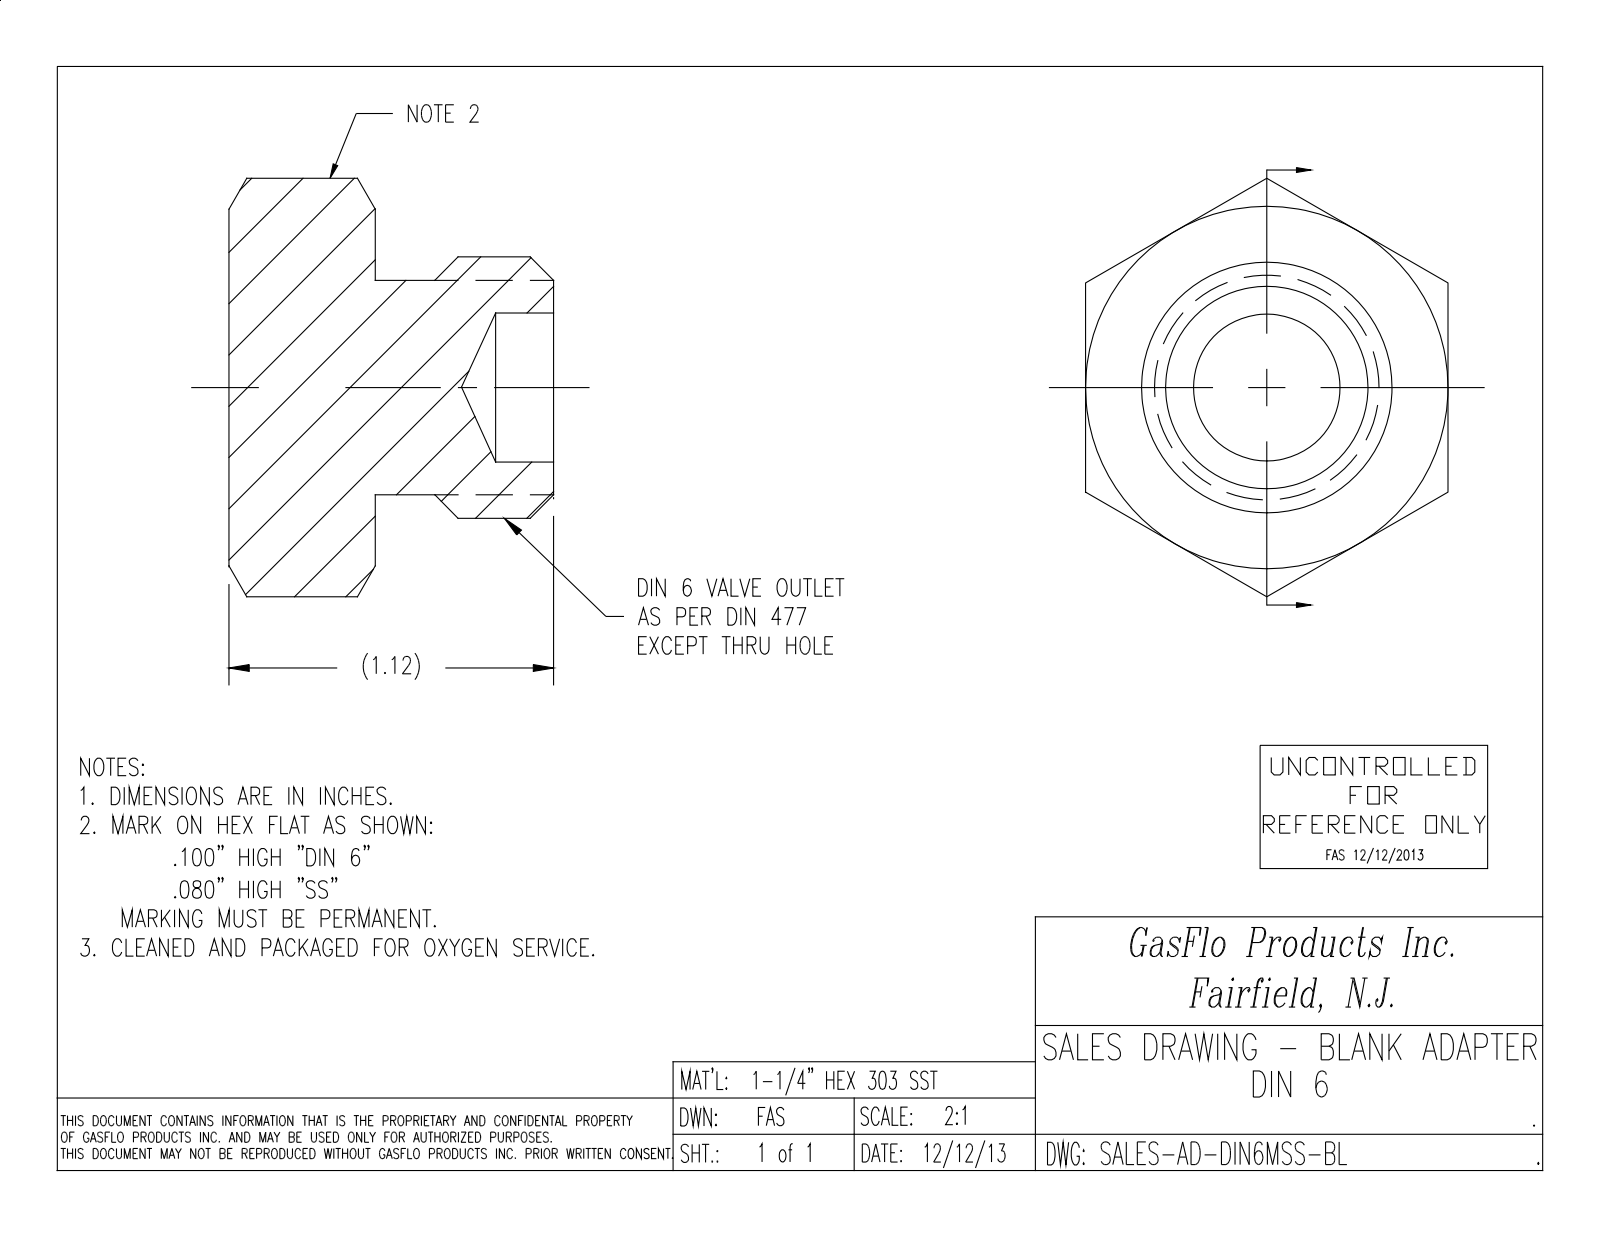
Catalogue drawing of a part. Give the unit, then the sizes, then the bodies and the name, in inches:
Units: inches
Overall size (bounding box): 1.443 × 1.25 × 1.12
Round holes (diameter × count): ⌀0.512 ×1
Round bosses / shafts (diameter × count): ⌀0.85 ×1, ⌀0.74 ×1
Main face-to-face distances: 0.505, 1.25, 1.25, 1.12, 0.615, 1.245, 0.103, 0.133, 0.031, 0.112
Volume: 0.905 in³ · Surface area: 7.484 in²
Bodies: 1 solid, 120 faces (44 planar, 13 cylindrical, 63 other)
Part name (STEP PRODUCT): AD-DIN6MSS-BL
STEP written by: SolidWorks 2018 (CONFIG_CONTROL_DESIGN)
